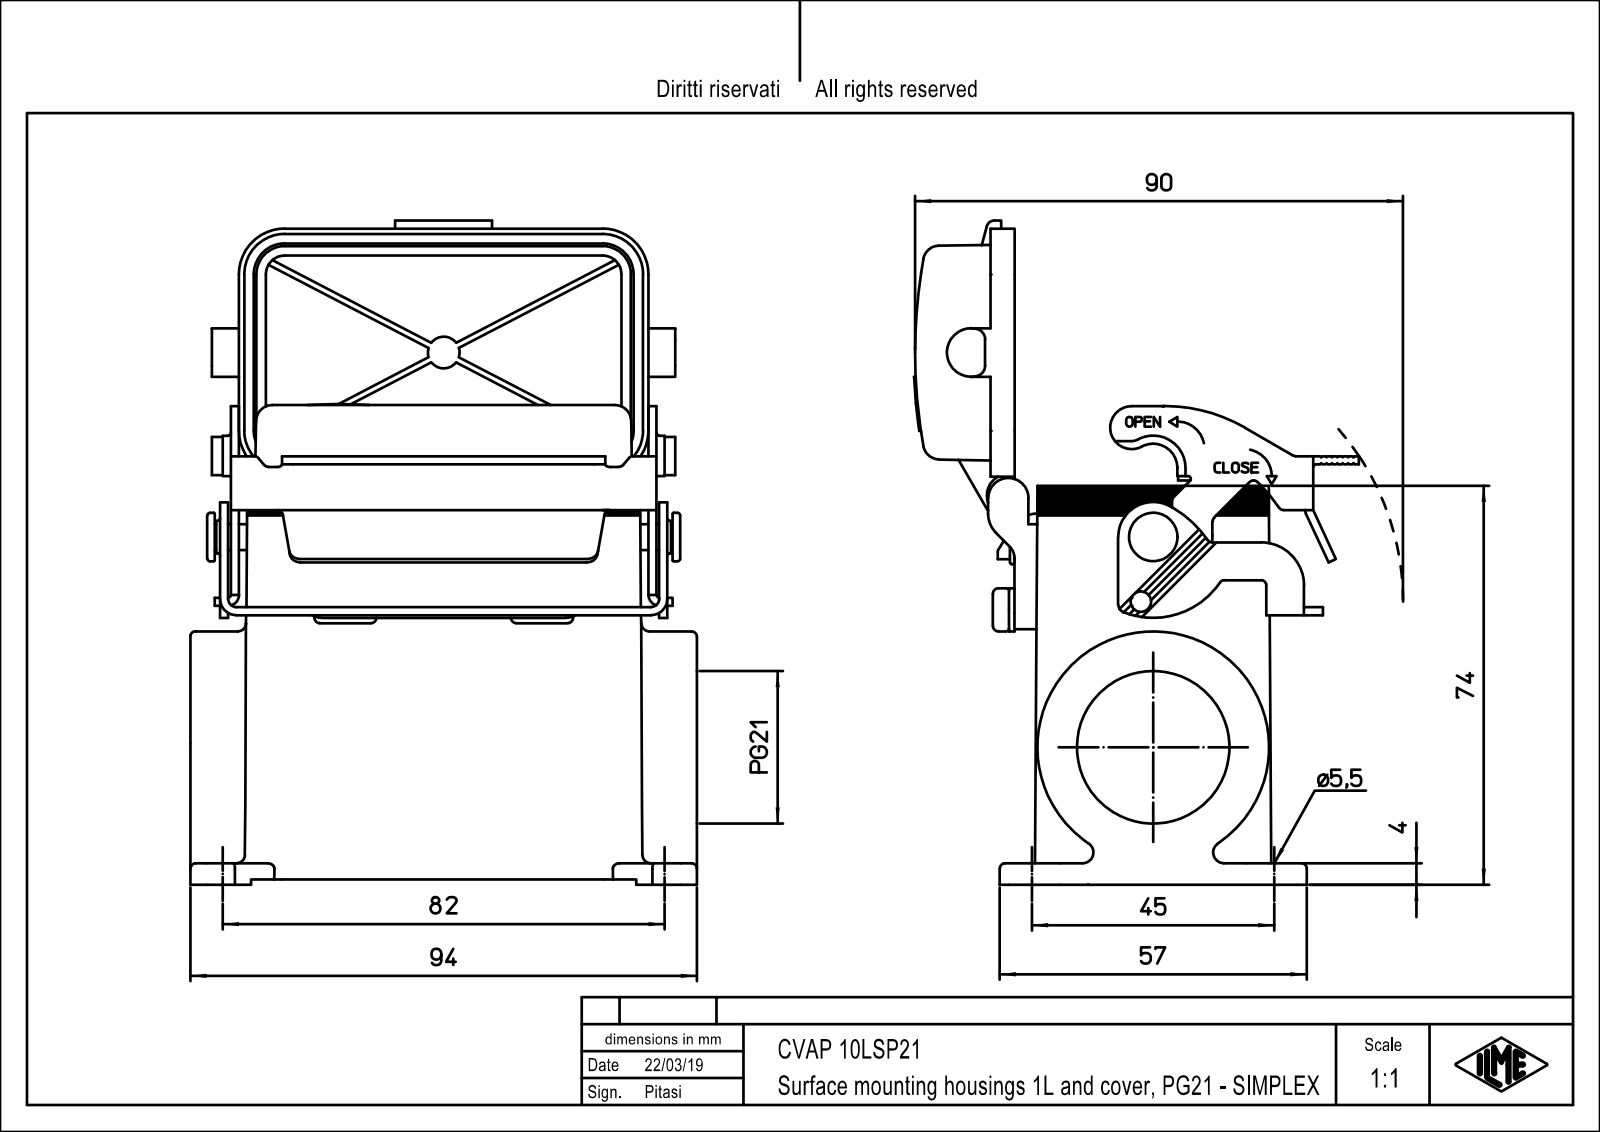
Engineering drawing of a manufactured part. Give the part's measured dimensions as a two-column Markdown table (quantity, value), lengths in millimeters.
| quantity | value |
| --- | --- |
| part name | CVAP_10_LSP21 |
| STEP written by | Creo Elements/Direct Modeling 18.1F 24-Jul-2014 (C) Parametric Technology GmbH (AUTOMOTIVE_DESIGN) |
| units | millimeters |
| bodies | 1 solid, 653 faces (352 planar, 265 cylindrical, 36 other) |
| overall size | 122.72 × 93.5 × 80.38 |
| volume | 119 574 mm³ |
| surface area | 70 265 mm² |
| round holes (diameter × count) | 2.46 × 4, 3 × 4, 5.5 × 4, 20.78 × 1, 26.78 × 1 |
| round bosses / shafts (diameter × count) | 0.8 × 3, 9 × 1, 8 × 1, 5 × 1, 2.4 × 1 |
| partial cylindrical surfaces (radius × count) | 0.25 × 16, 0.33 × 15, 1 × 15, 0.5 × 12, 1.5 × 12, 2 × 12, 1.4 × 6, 2.8 × 6 |
| main face-to-face distances | 4, 40.5, 1.4, 2, 36.5, 44.5, 10, 60, 6.75, 72.75 |
| hole center spacings | 15.4, 38.11, 70.08, 78.27, 27, 45, 57, 63.07 |
